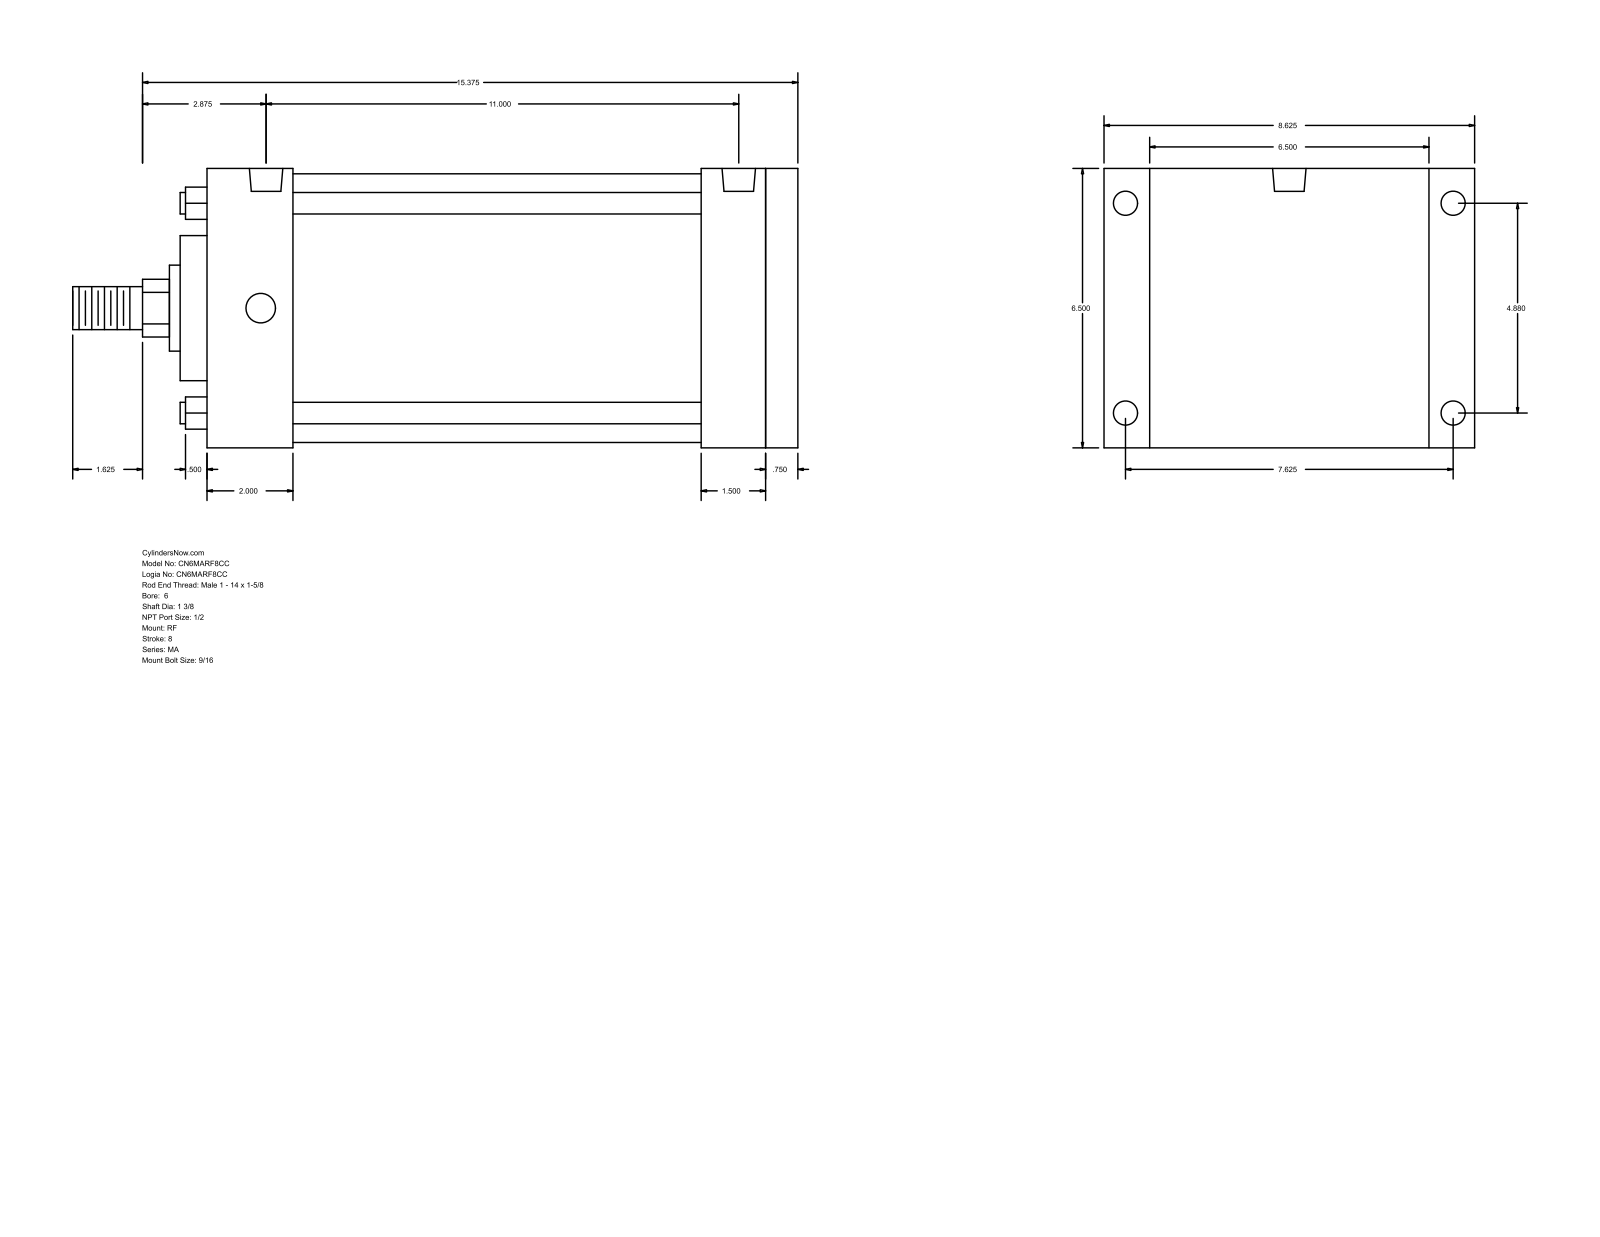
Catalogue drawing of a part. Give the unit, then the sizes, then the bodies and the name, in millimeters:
Units: millimetres
Overall size (bounding box): 431.8 × 219.07 × 165.1
Round holes (diameter × count): ⌀14.29 ×4, ⌀17.46 ×4, ⌀19.77 ×2
Round bosses / shafts (diameter × count): ⌀12.7 ×4, ⌀158.75 ×1, ⌀85.72 ×1, ⌀50.8 ×1, ⌀34.92 ×1, ⌀25.4 ×1
Partial cylindrical surfaces — rounded edges, fillets, slot ends (radius × count): R17.06 ×1
Main face-to-face distances: 165.1, 352.42, 333.38, 19.04, 38.1, 50.8, 282.58, 301.62, 295.28, 244.48
Hole centre spacings: 123.96, 193.68, 229.95, 282.58, 3.18, 279.4
Bodies: 0 solids, 94 faces (65 planar, 29 cylindrical, 0 other)
Part name (STEP PRODUCT): MA_RF__0600_1.375
STEP written by: GSSL Pune (CONFIG_CONTROL_DESIGN)
